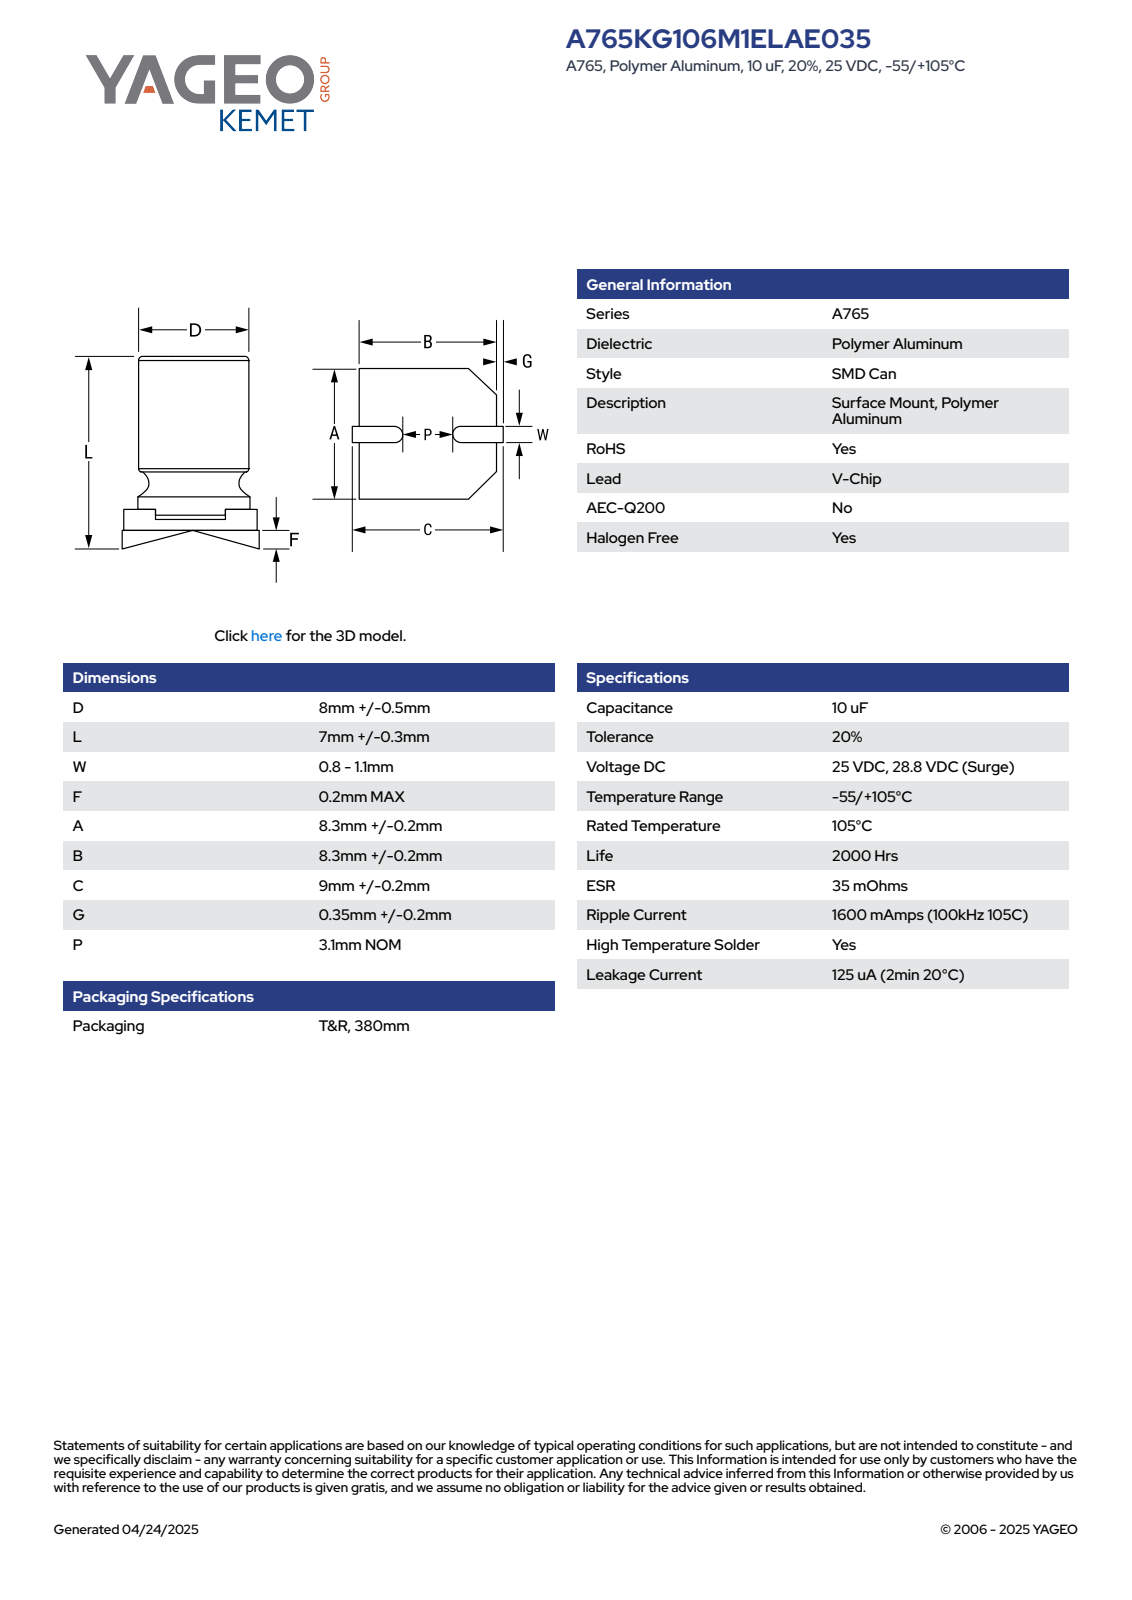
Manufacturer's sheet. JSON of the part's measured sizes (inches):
{"part_name": "CAC_KS_8X7_D8.5L7.3W1.1F0.2A8.5B8.5C9.2P3.1", "step_written_by": "SolidWorks 2014 (AUTOMOTIVE_DESIGN)", "units": "inches", "bodies": {"solids": 5, "faces": 76, "planar": 59, "cylindrical": 11, "other": 6}, "overall_size": [0.362, 0.335, 0.287], "volume_in3": 0.023, "surface_area_in2": 0.742, "round_bosses_or_shafts": [[0.32, 1]], "partial_cylinders_radius": [[0.008, 2], [0.133, 1], [0.167, 1]], "face_to_face_distances": [0.015, 0.28, 0.265, 0.335, 0.072, 0.057, 0.208, 0.022, 0.08, 0.287]}
